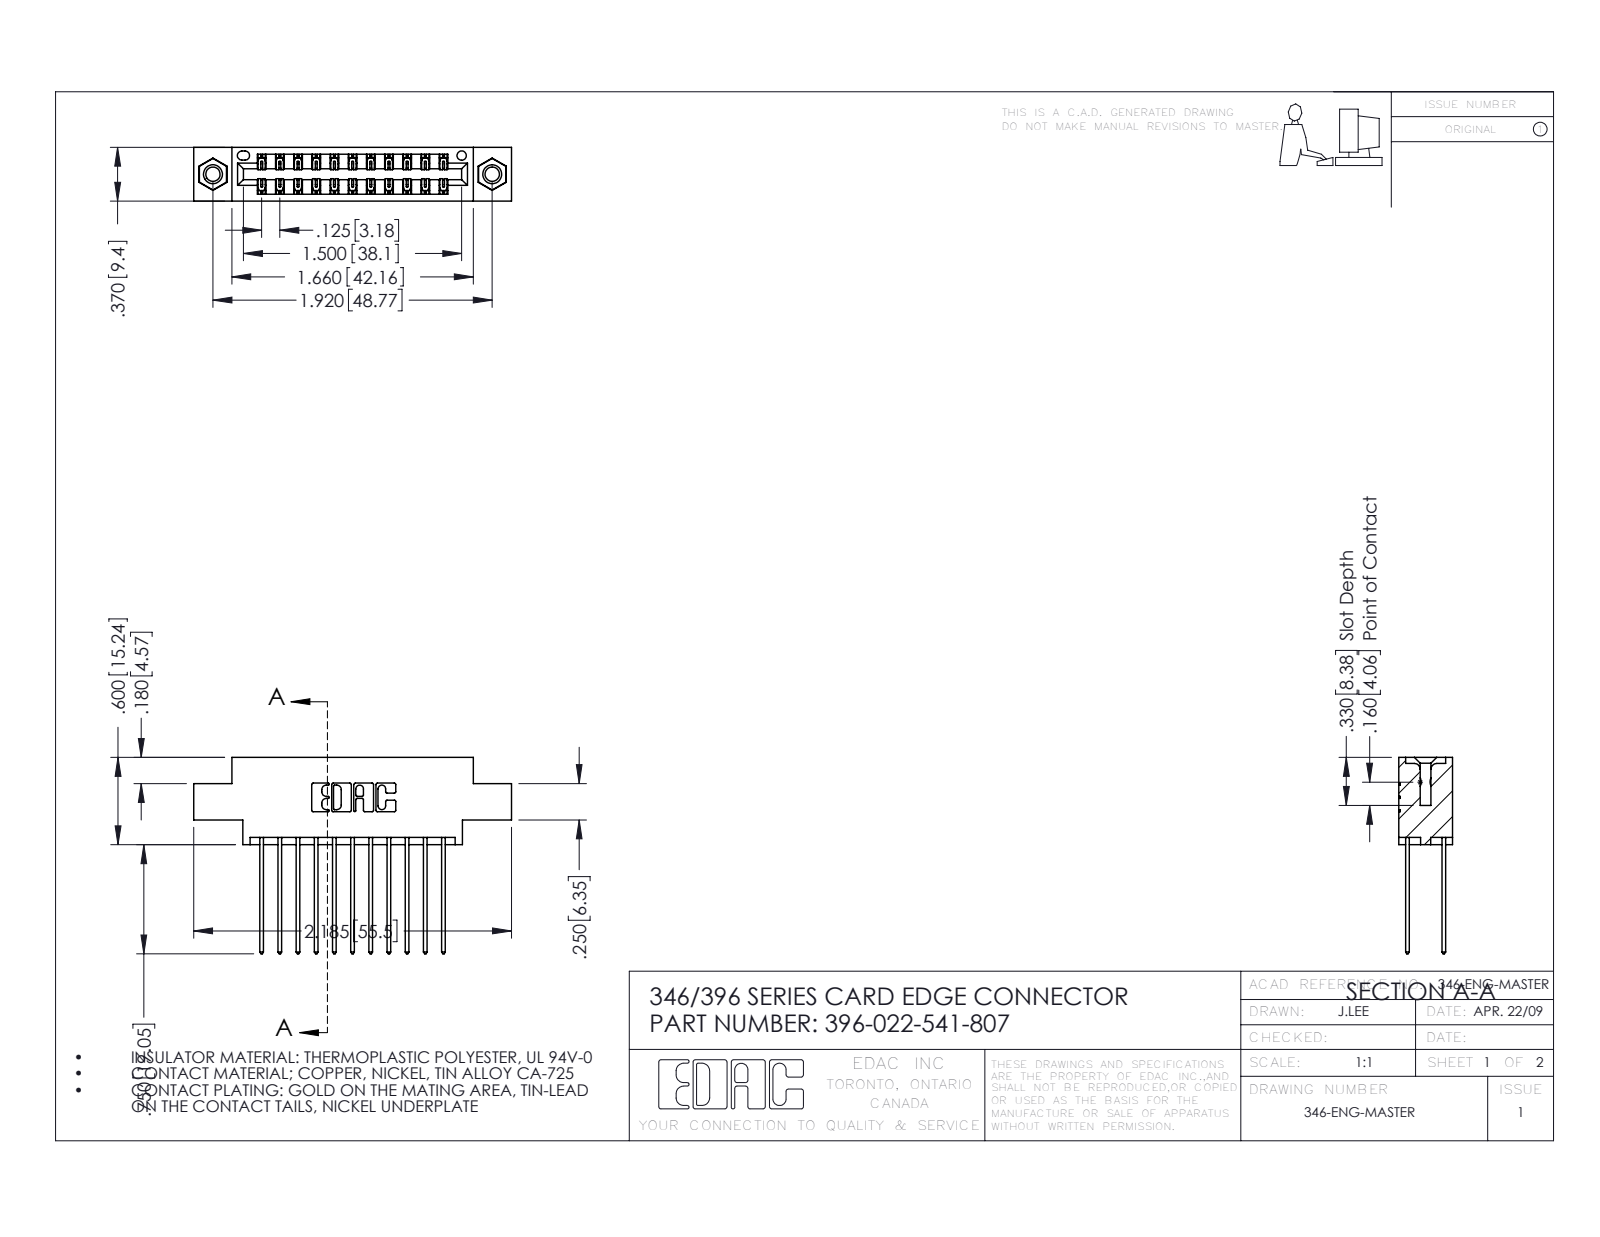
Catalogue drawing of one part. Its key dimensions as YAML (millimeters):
part_name: "345-292-001_345-293-141; 345-250-001_345-250-005-103; 346 Part_0.170 Offset - 0.156 Dia-TI; 396-022-541-807"
step_written_by: "SolidWorks 2016 (CONFIG_CONTROL_DESIGN)"
units: millimeters
bodies: {solids: 25, faces: 1330, planar: 882, cylindrical: 432, other: 16}
overall_size: [55.5, 34.3, 9.4]
volume: 5130
surface_area: 7381
round_holes:
  - {diameter: 2.5, count: 2}
  - {diameter: 3.2, count: 2}
  - {diameter: 4, count: 2}
  - {diameter: 1.6, count: 1}
round_bosses_or_shafts:
  - {diameter: 3.9, count: 2}
partial_cylinders:
  - {radius: 0.2, count: 33}
  - {radius: 0.3, count: 22}
  - {radius: 0.3, count: 22}
  - {radius: 0.2, count: 6}
  - {radius: 0.8, count: 6}
  - {radius: 0.7, count: 3}
  - {radius: 0.4, count: 2}
  - {radius: 0.6, count: 2}
face_to_face_distances: [6.4, 1.2, 8.2, 9.4, 1.8, 7.6, 0.6, 7, 5.6, 3.8]
hole_center_spacings: [6.2, 43.6, 48.8]
